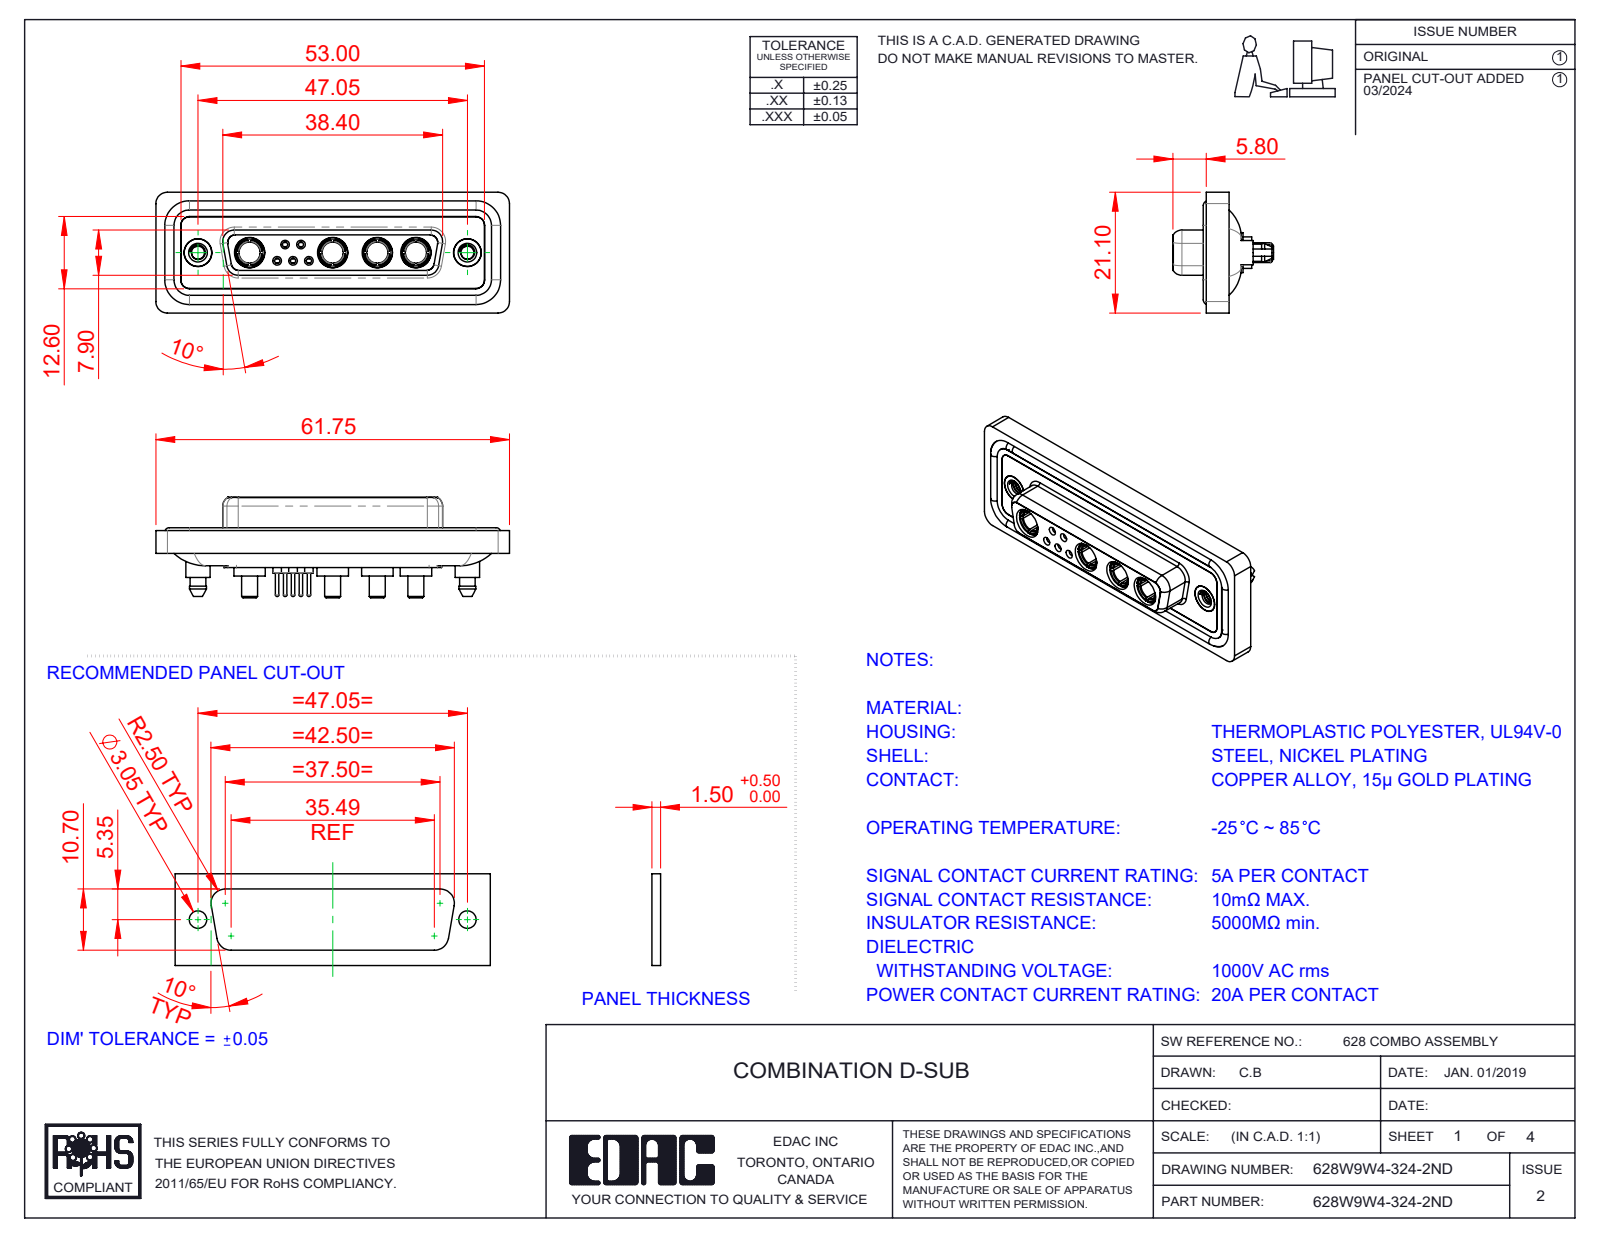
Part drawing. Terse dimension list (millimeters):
name: 628W9W4-324-2ND; 628Combo Shell Rear_25 Contacts; 628Combo Contact Row 2_24; 628Combo Threaded Boardlock_D (+5 more)
written by: SolidWorks 2023 (CONFIG_CONTROL_DESIGN)
unit: mm
bodies: 20 solids, 1023 faces (312 planar, 423 cylindrical, 288 other)
size: 61.75 × 21.1 × 17.55
volume: 8 359 mm³; area: 13 901 mm²
holes: 6× ⌀4.85, 5× ⌀0.9, 5× ⌀1.1, 5× ⌀1.5, 5× ⌀2, 4× ⌀3.7, 4× ⌀5.3, 3× ⌀1.6, 2× ⌀1.7, 2× ⌀2.26, 2× ⌀4, 2× ⌀4.05
bosses: 6× ⌀1.6, 5× ⌀2.2, 5× ⌀0.6, 4× ⌀5.5, 4× ⌀5.2, 4× ⌀4.96, 4× ⌀4.75, 4× ⌀3.75
rounds: 24× R1.5, 18× R2, 10× R1.6, 8× R1.35, 4× R0.25, 4× R0.5, 4× R0.6, 4× R0.65
face distances: 0.4, 1.8, 7.45, 5.65, 0.5, 7.05, 6.6, 1.6, 1.1, 2.9
hole spacings: 3.16, 2.77, 5.03, 2.76, 4.4, 5.02, 5.54, 5.73
